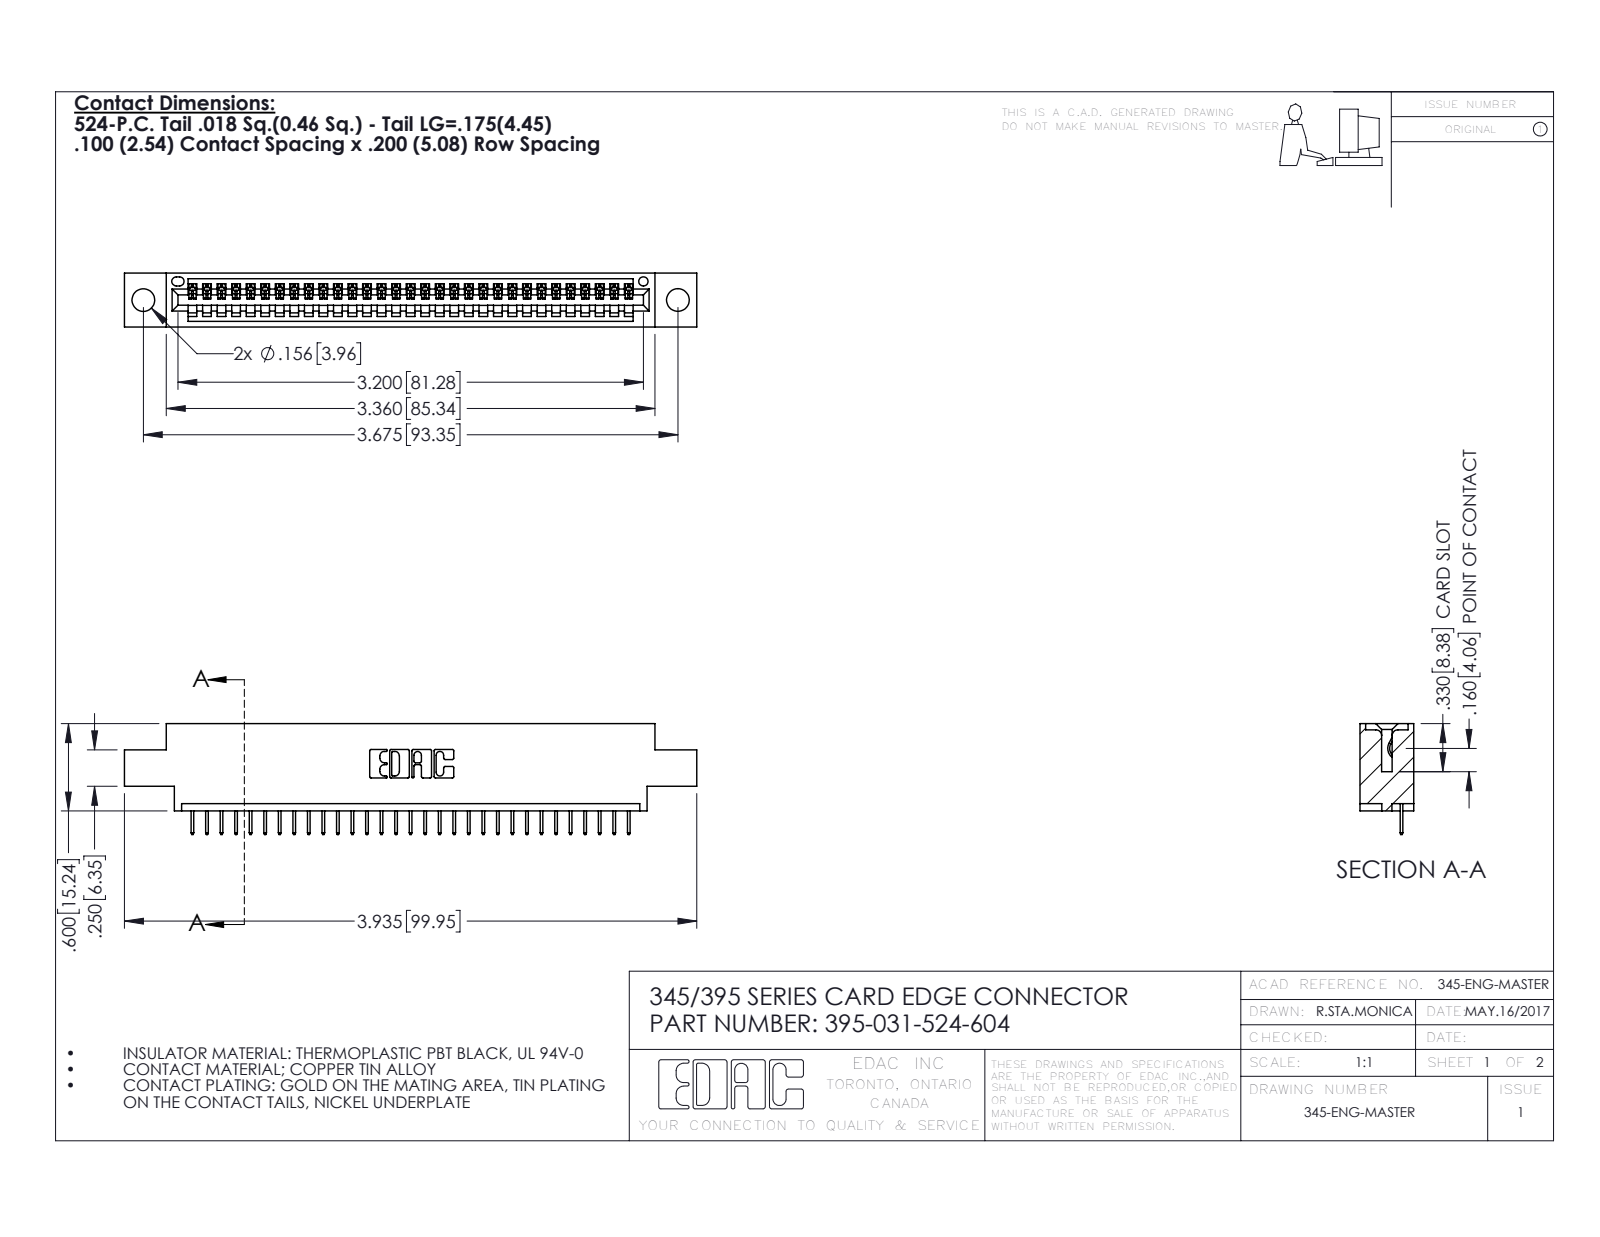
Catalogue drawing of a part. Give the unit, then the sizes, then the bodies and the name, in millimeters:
Units: millimetres
Overall size (bounding box): 99.9 × 19.4 × 9.4
Round holes (diameter × count): ⌀4 ×2, ⌀1.6 ×1
Partial cylindrical surfaces — rounded edges, fillets, slot ends (radius × count): R0.2 ×62, R0.3 ×22, R0.2 ×6, R0.8 ×6, R0.7 ×3, R0.8 ×2, R1 ×2, R0.4 ×1
Main face-to-face distances: 1.8, 7.6, 9.4, 5.1, 2.5, 6.9, 0.6, 5.7, 1.8, 4.4
Hole centre spacings: 6.9, 87.4, 93.3
Volume: 9 080 mm³ · Surface area: 11 460 mm²
Bodies: 32 solids, 2052 faces (1510 planar, 542 cylindrical, 0 other)
Part name (STEP PRODUCT): 345 Part_0.170 Offset - 0.156 Dia-TH; 345-292-001_345-293-124; 395-031-524-604
STEP written by: SolidWorks 2016 (CONFIG_CONTROL_DESIGN)
